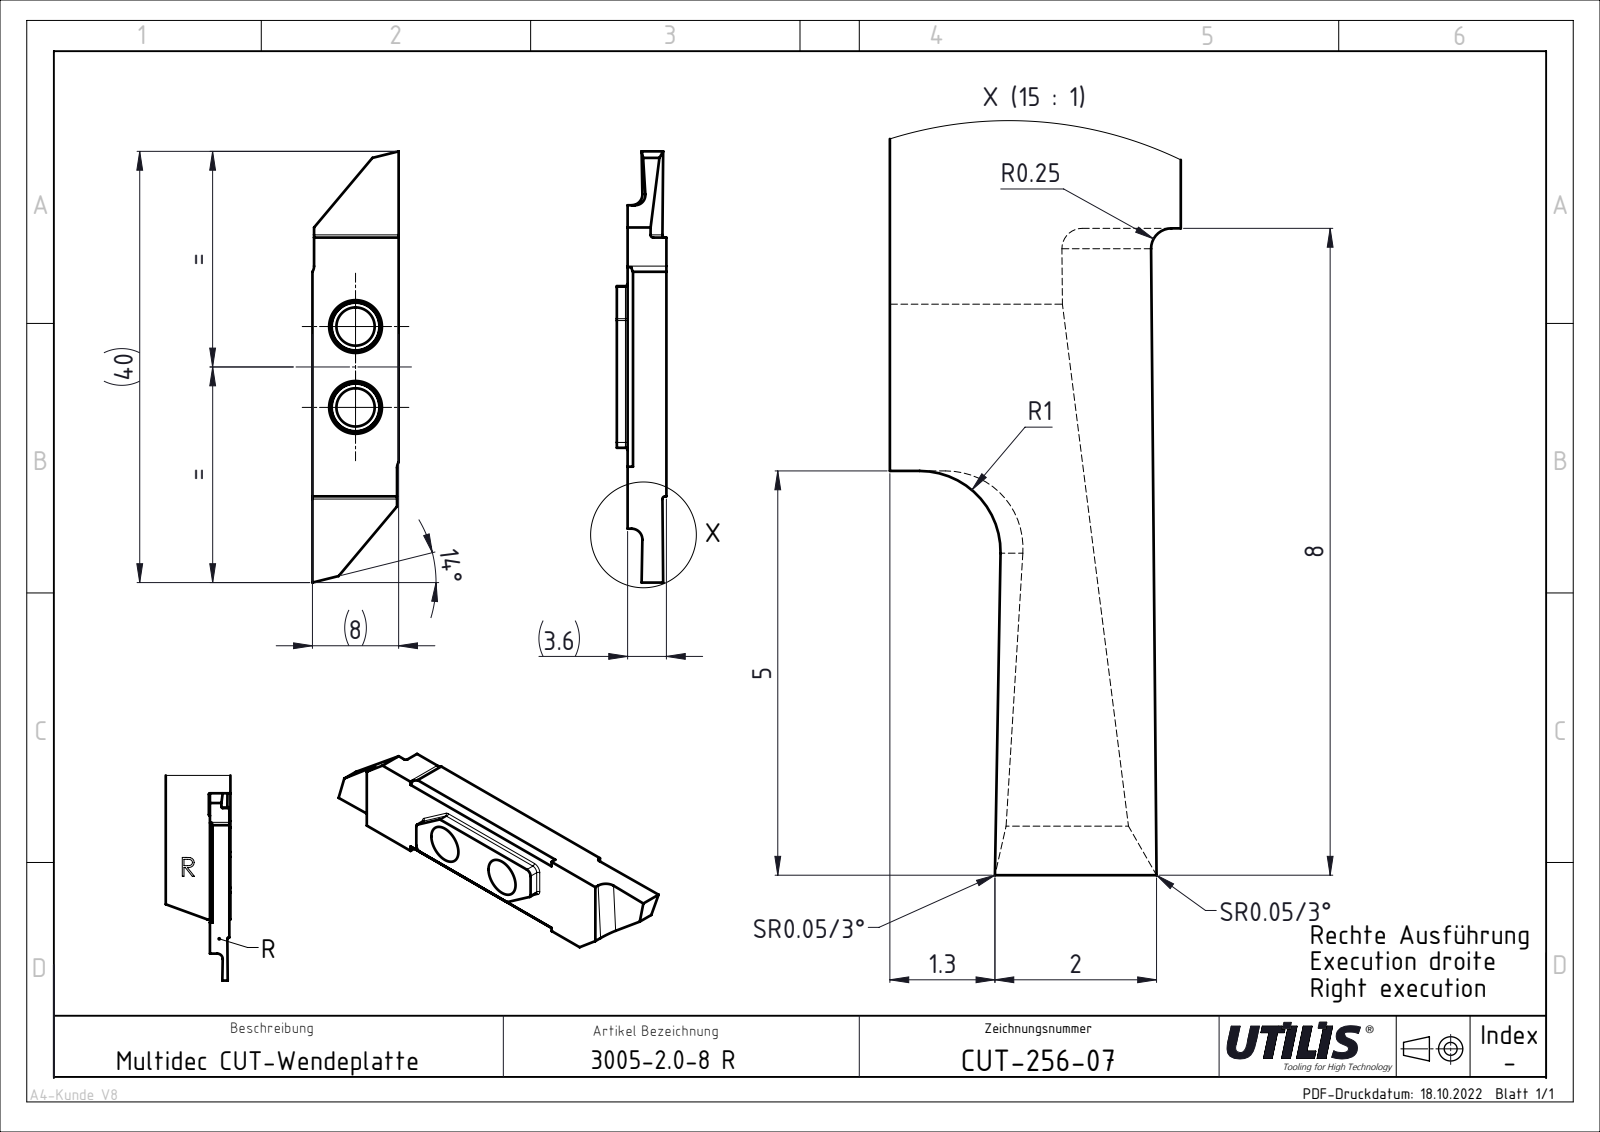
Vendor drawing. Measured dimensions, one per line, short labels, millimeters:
name: CUT-256-07
written by: SolidWorks 2016 (AUTOMOTIVE_DESIGN)
unit: mm
bodies: 1 solid, 38 faces (24 planar, 14 cylindrical, 0 other)
size: 40 × 8 × 3.5
volume: 819 mm³; area: 859 mm²
holes: 2× ⌀3.55
rounds: 4× R0.15, 4× R1, 2× R0.4
face distances: 3.5, 8, 7.85, 22.54, 7.7, 5, 35, 40, 30, 38.98
hole spacings: 7.5
